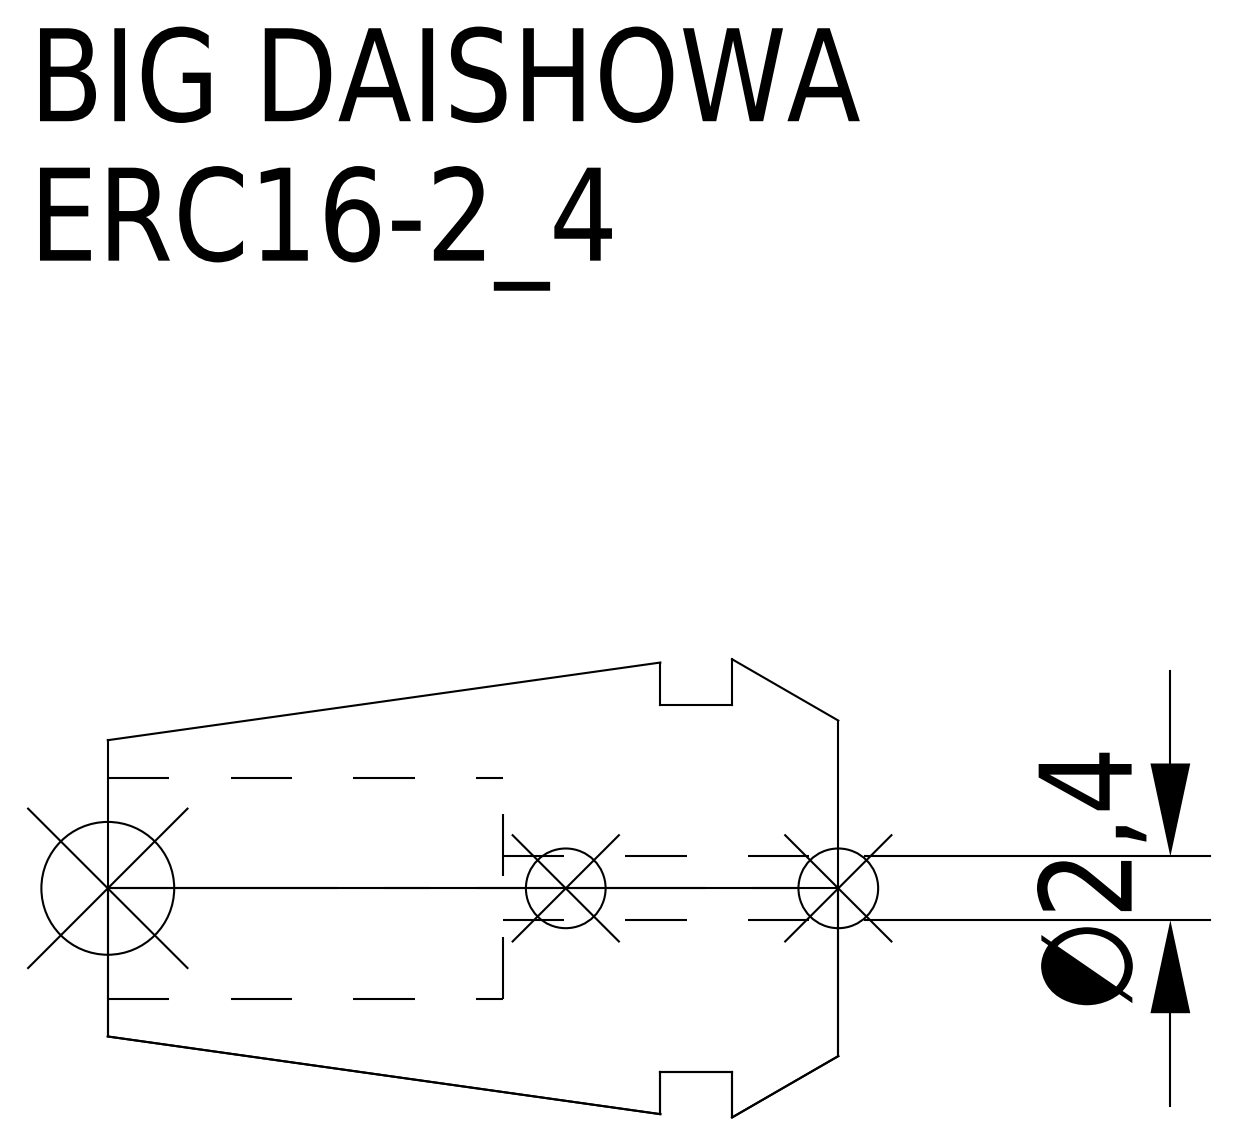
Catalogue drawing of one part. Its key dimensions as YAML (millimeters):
part_name: "ERC16-2_4"
step_written_by: "CREO PARAMETRIC BY PTC INC, 2016380 (AUTOMOTIVE_DESIGN)"
units: millimeters
bodies: {solids: 1, faces: 15, planar: 5, cylindrical: 6, other: 4}
overall_size: [27.5, 17.25, 17.25]
volume: 3533
surface_area: 2121
round_holes:
  - {diameter: 2.4, count: 1}
  - {diameter: 8.3, count: 1}
round_bosses_or_shafts:
  - {diameter: 13.8, count: 1}
face_to_face_distances: [4, 6.7, 2.7, 12.63, 8.63, 5.93, 27.5, 23.5, 20.8, 14.87]
